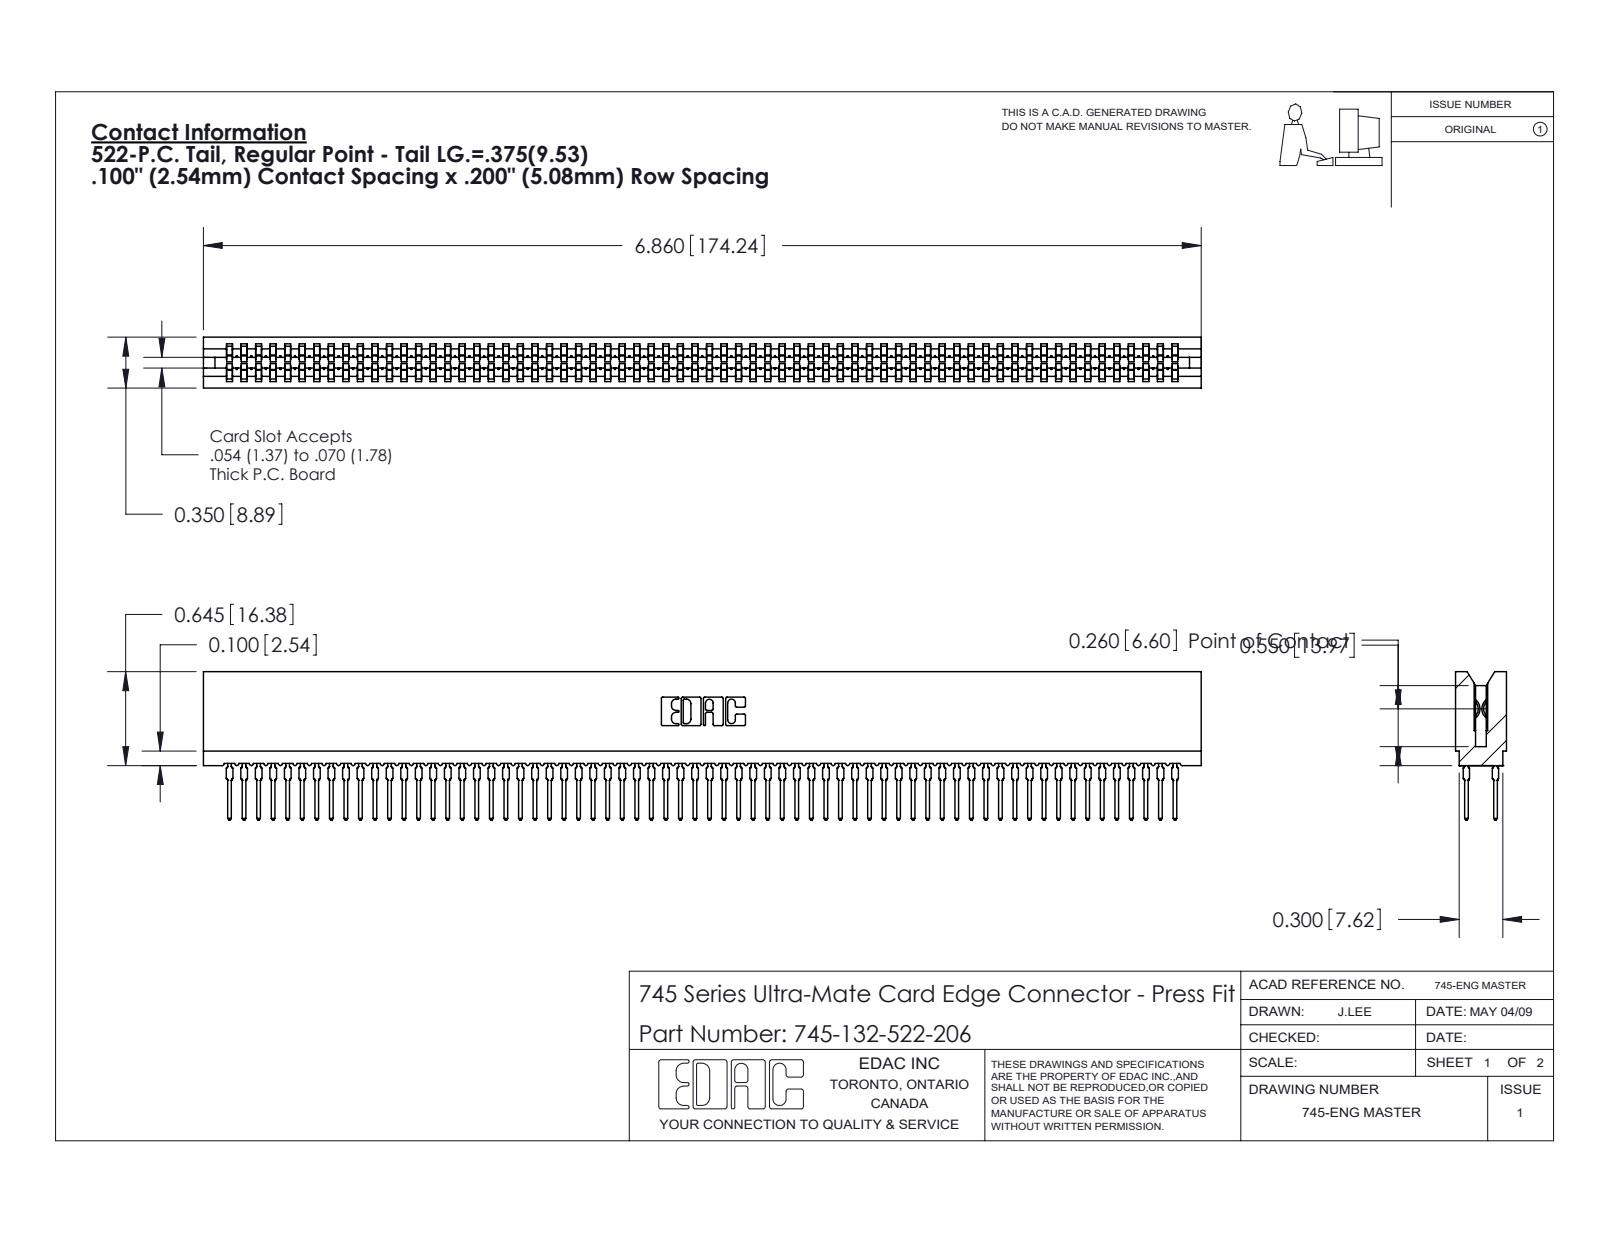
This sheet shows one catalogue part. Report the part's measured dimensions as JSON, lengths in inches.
{"part_name": "745 Part_Insulator Option - 06; 745-132-522-206; 745-292-001_522", "step_written_by": "SolidWorks 2020 (CONFIG_CONTROL_DESIGN)", "units": "inches", "bodies": {"solids": 133, "faces": 11910, "planar": 6128, "cylindrical": 2350, "other": 3432}, "overall_size": [6.86, 1.021, 0.35], "volume_in3": 0.956, "surface_area_in2": 50.97, "partial_cylinders_radius": [[0.021, 264], [0.015, 132], [0.01, 22], [0.005, 8], [0.011, 8], [0.007, 6], [0.031, 6], [0.026, 3]], "face_to_face_distances": [0.35, 0.063, 0.287, 0.045, 0.305, 0.018, 0.243, 0.138, 0.212, 0.093]}
